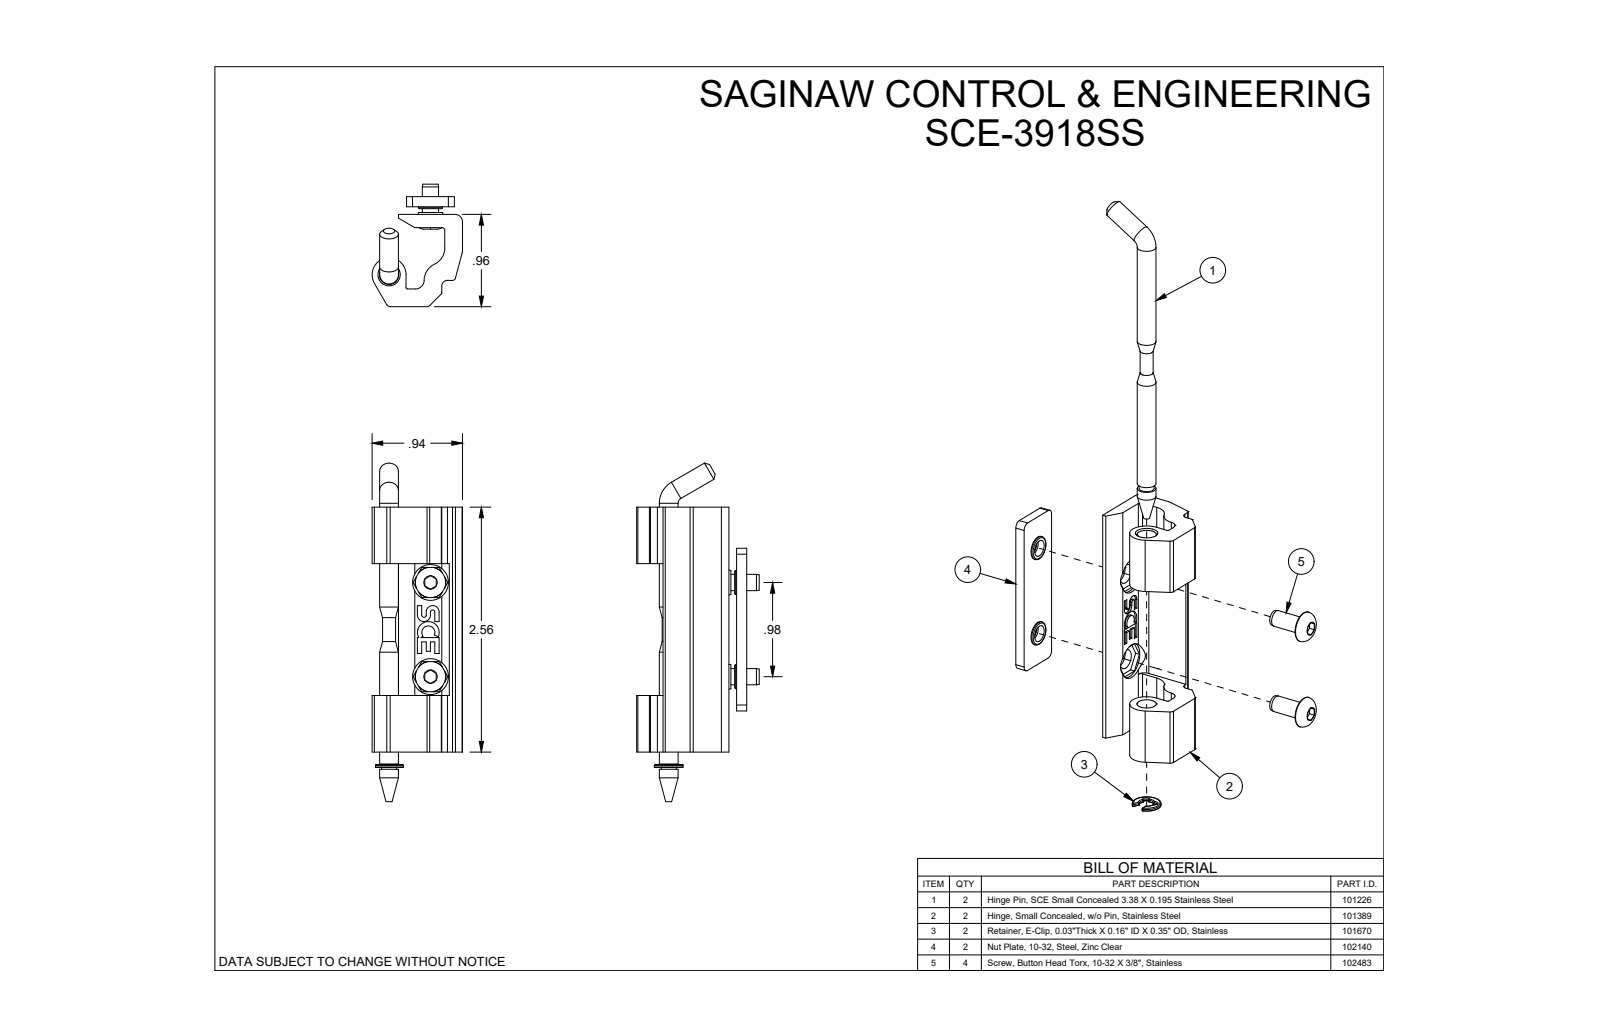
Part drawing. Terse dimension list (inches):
name: SCE-3918SS
written by: SolidWorks 2019 (CONFIG_CONTROL_DESIGN)
unit: in
bodies: 6 solids, 211 faces (111 planar, 67 cylindrical, 33 other)
size: 3.537 × 1.28 × 0.945
volume: 0.869 in³; area: 16.68 in²
holes: 2× ⌀0.172, 2× ⌀0.205, 2× ⌀0.244, 2× ⌀0.375, 1× ⌀0.203
bosses: 2× ⌀0.25, 2× ⌀0.196, 2× ⌀0.17, 1× ⌀0.3, 1× ⌀0.157, 1× ⌀0.136
rounds: 3× R0.01, 3× R0.068, 2× R0.005, 2× R0.016, 2× R0.03, 2× R0.04, 2× R0.062, 2× R0.063
face distances: 0.138, 0.08, 0.106, 0.186, 0.591, 1.969, 0.324, 0.218, 1.15, 1.044
hole spacings: 0.984
